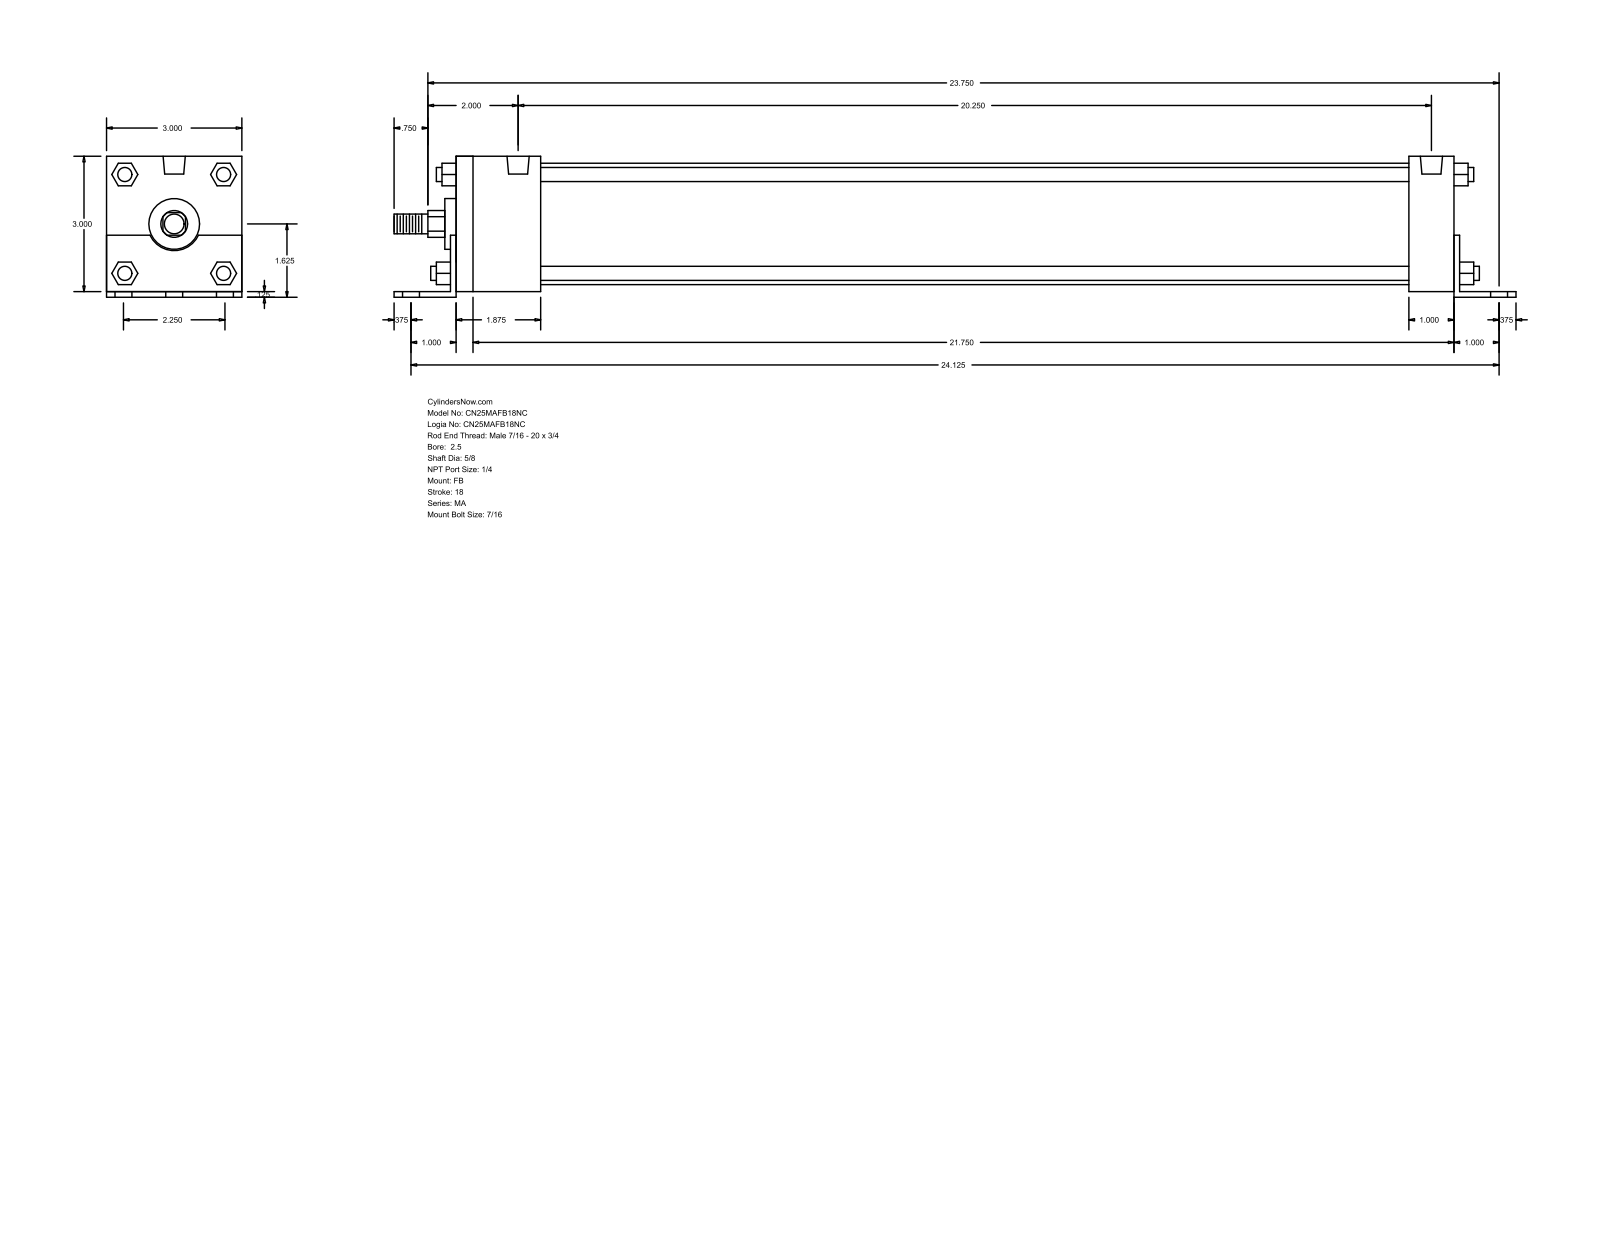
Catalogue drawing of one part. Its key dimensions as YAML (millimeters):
part_name: "MA_FB__0250_0.625"
step_written_by: "GSSL Pune (CONFIG_CONTROL_DESIGN)"
units: millimeters
bodies: {solids: 0, faces: 140, planar: 105, cylindrical: 35, other: 0}
overall_size: [631.83, 79.38, 76.2]
round_holes:
  - {diameter: 11.11, count: 6}
  - {diameter: 7.94, count: 4}
  - {diameter: 12.49, count: 2}
round_bosses_or_shafts:
  - {diameter: 7.94, count: 4}
  - {diameter: 68.33, count: 1}
  - {diameter: 28.57, count: 1}
  - {diameter: 15.88, count: 1}
  - {diameter: 11.11, count: 1}
partial_cylinders:
  - {radius: 7.54, count: 1}
  - {radius: 15.05, count: 1}
face_to_face_distances: [76.2, 3.17, 79.37, 561.97, 568.32, 3.18, 565.14, 47.62, 25.4, 565.15]
hole_center_spacings: [28.57, 613.45, 612.78, 47.62, 57.14, 66.75, 514.35, 553.19]
